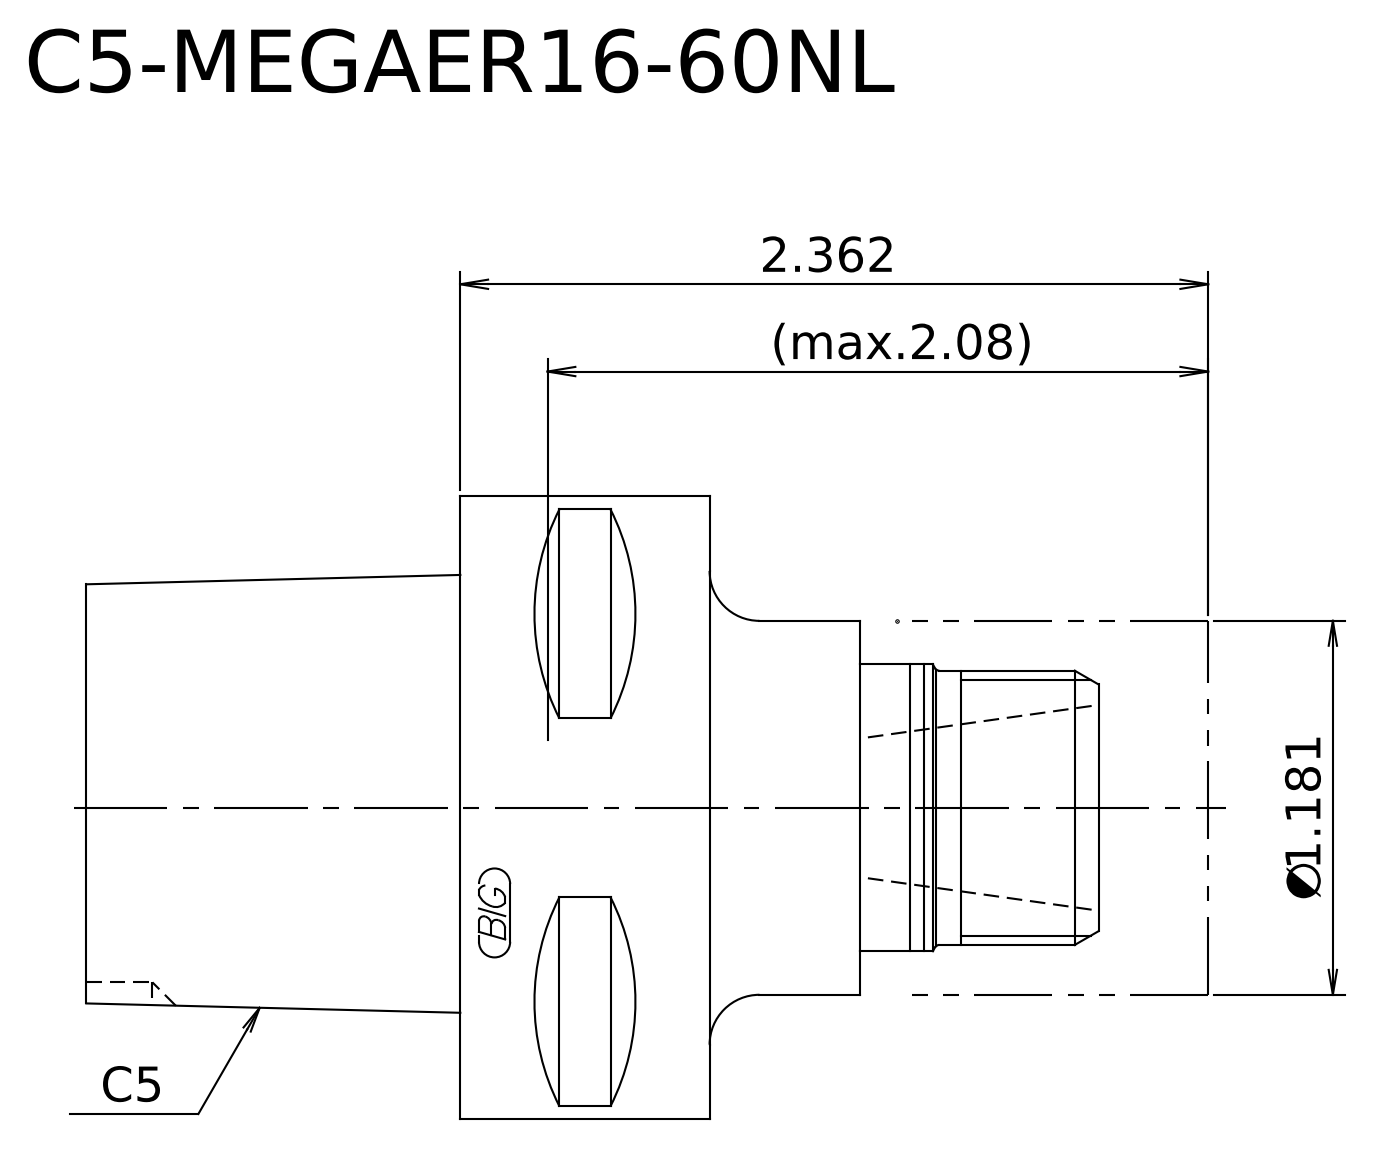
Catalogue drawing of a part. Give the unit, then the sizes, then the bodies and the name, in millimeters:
Units: millimetres
Overall size (bounding box): 90 × 50 × 50
Round bosses / shafts (diameter × count): ⌀50 ×1, ⌀30 ×1, ⌀23 ×1, ⌀22 ×1
Main face-to-face distances: 30, 20, 50, 15, 35, 65, 25, 40, 60, 90
Volume: 100 924 mm³ · Surface area: 16 205 mm²
Bodies: 2 solids, 16 faces (7 planar, 5 cylindrical, 4 other)
STEP written by: Kubotek KeyCreator 2011 V10.0.2 (22737) (automotive_design)
